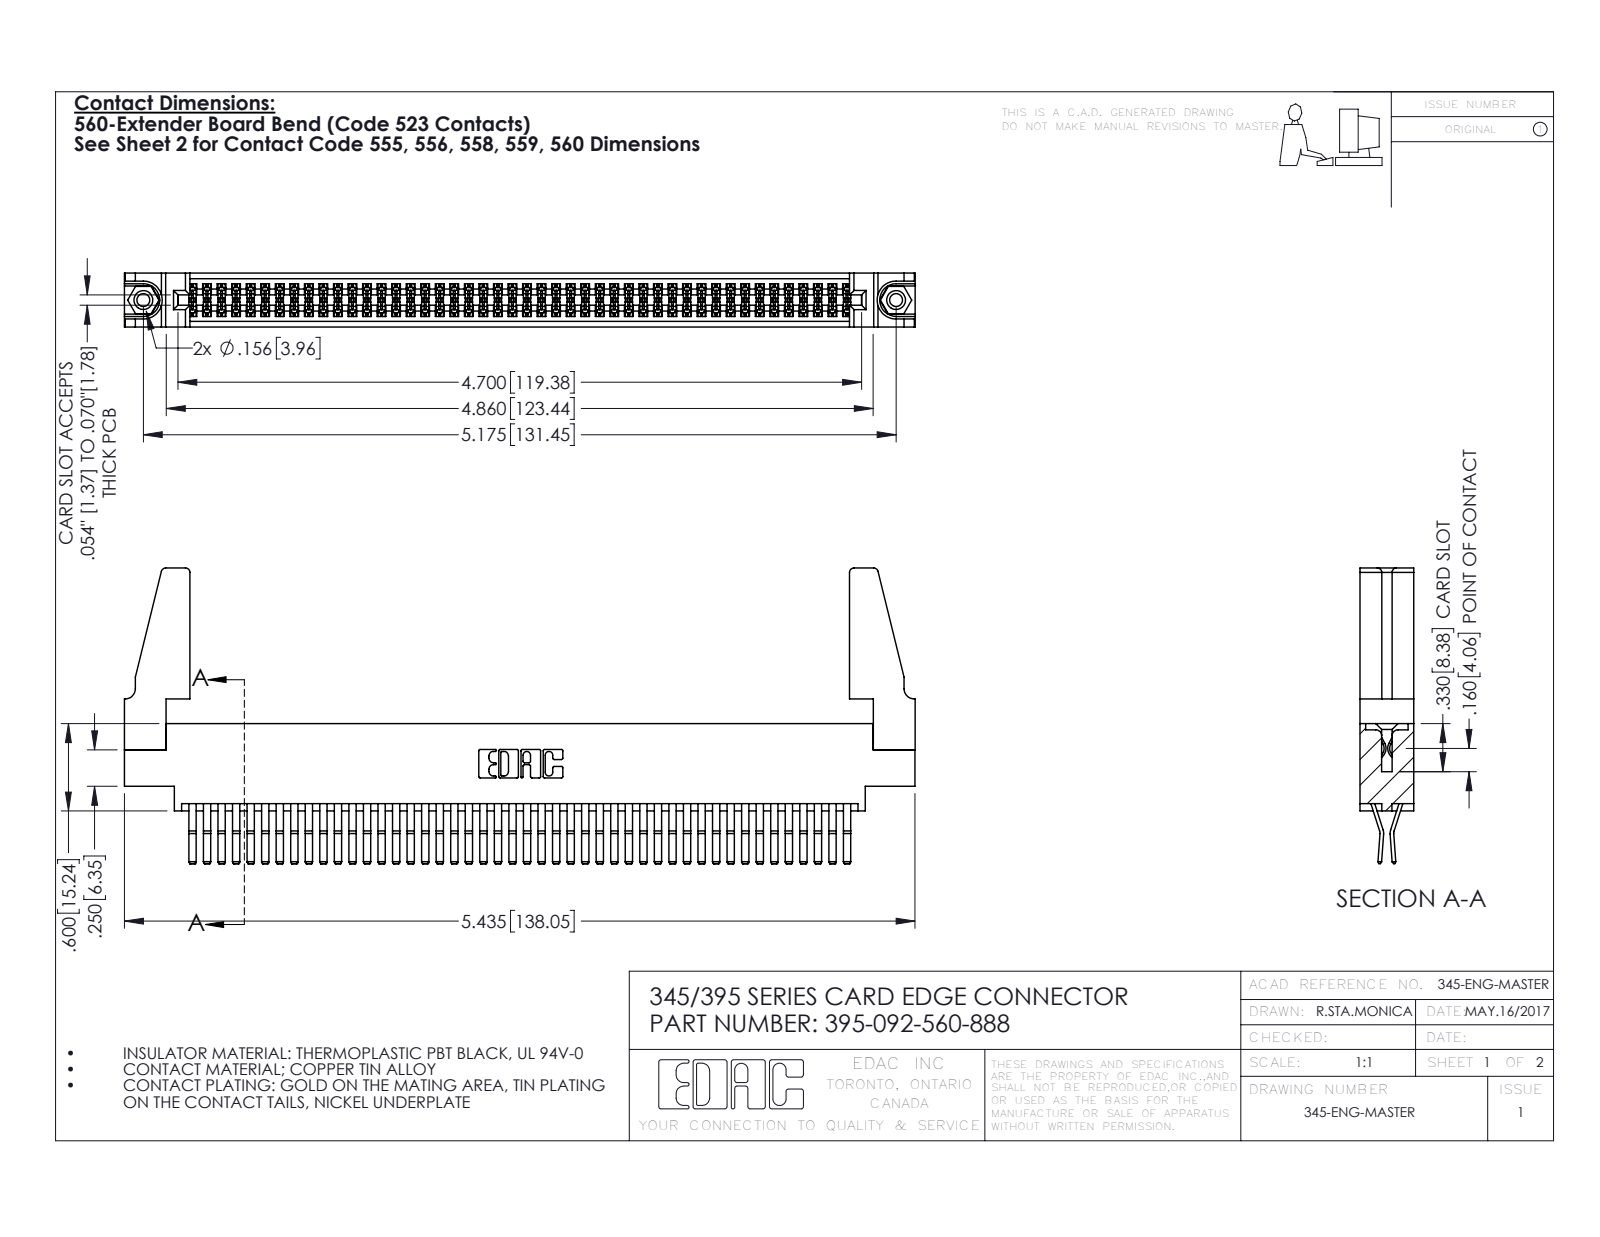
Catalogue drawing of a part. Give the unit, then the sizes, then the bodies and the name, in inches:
Units: inches
Overall size (bounding box): 5.436 × 2.032 × 0.37
Round holes (diameter × count): ⌀0.089 ×2, ⌀0.125 ×2, ⌀0.156 ×2, ⌀0.064 ×1
Round bosses / shafts (diameter × count): ⌀0.155 ×2
Partial cylindrical surfaces — rounded edges, fillets, slot ends (radius × count): R0.006 ×138, R0.01 ×22, R0.03 ×8, R0.007 ×6, R0.031 ×6, R0.026 ×3, R0.01 ×2, R0.014 ×2
Main face-to-face distances: 0.072, 0.298, 0.025, 0.37, 0.2, 0.098, 0.272, 0.225, 0.175, 0.149
Hole centre spacings: 0.27, 4.939, 5.175
Volume: 1.049 in³ · Surface area: 39.52 in²
Bodies: 97 solids, 5038 faces (3192 planar, 1830 cylindrical, 16 other)
Part name (STEP PRODUCT): 345 Part_0.170 Offset - 0.156 Dia-TH; 345-250-001_345-250-001-102; 345-220-078_345-220-088; 345-292-001_560 Tail (+1 more)
STEP written by: SolidWorks 2016 (CONFIG_CONTROL_DESIGN)
